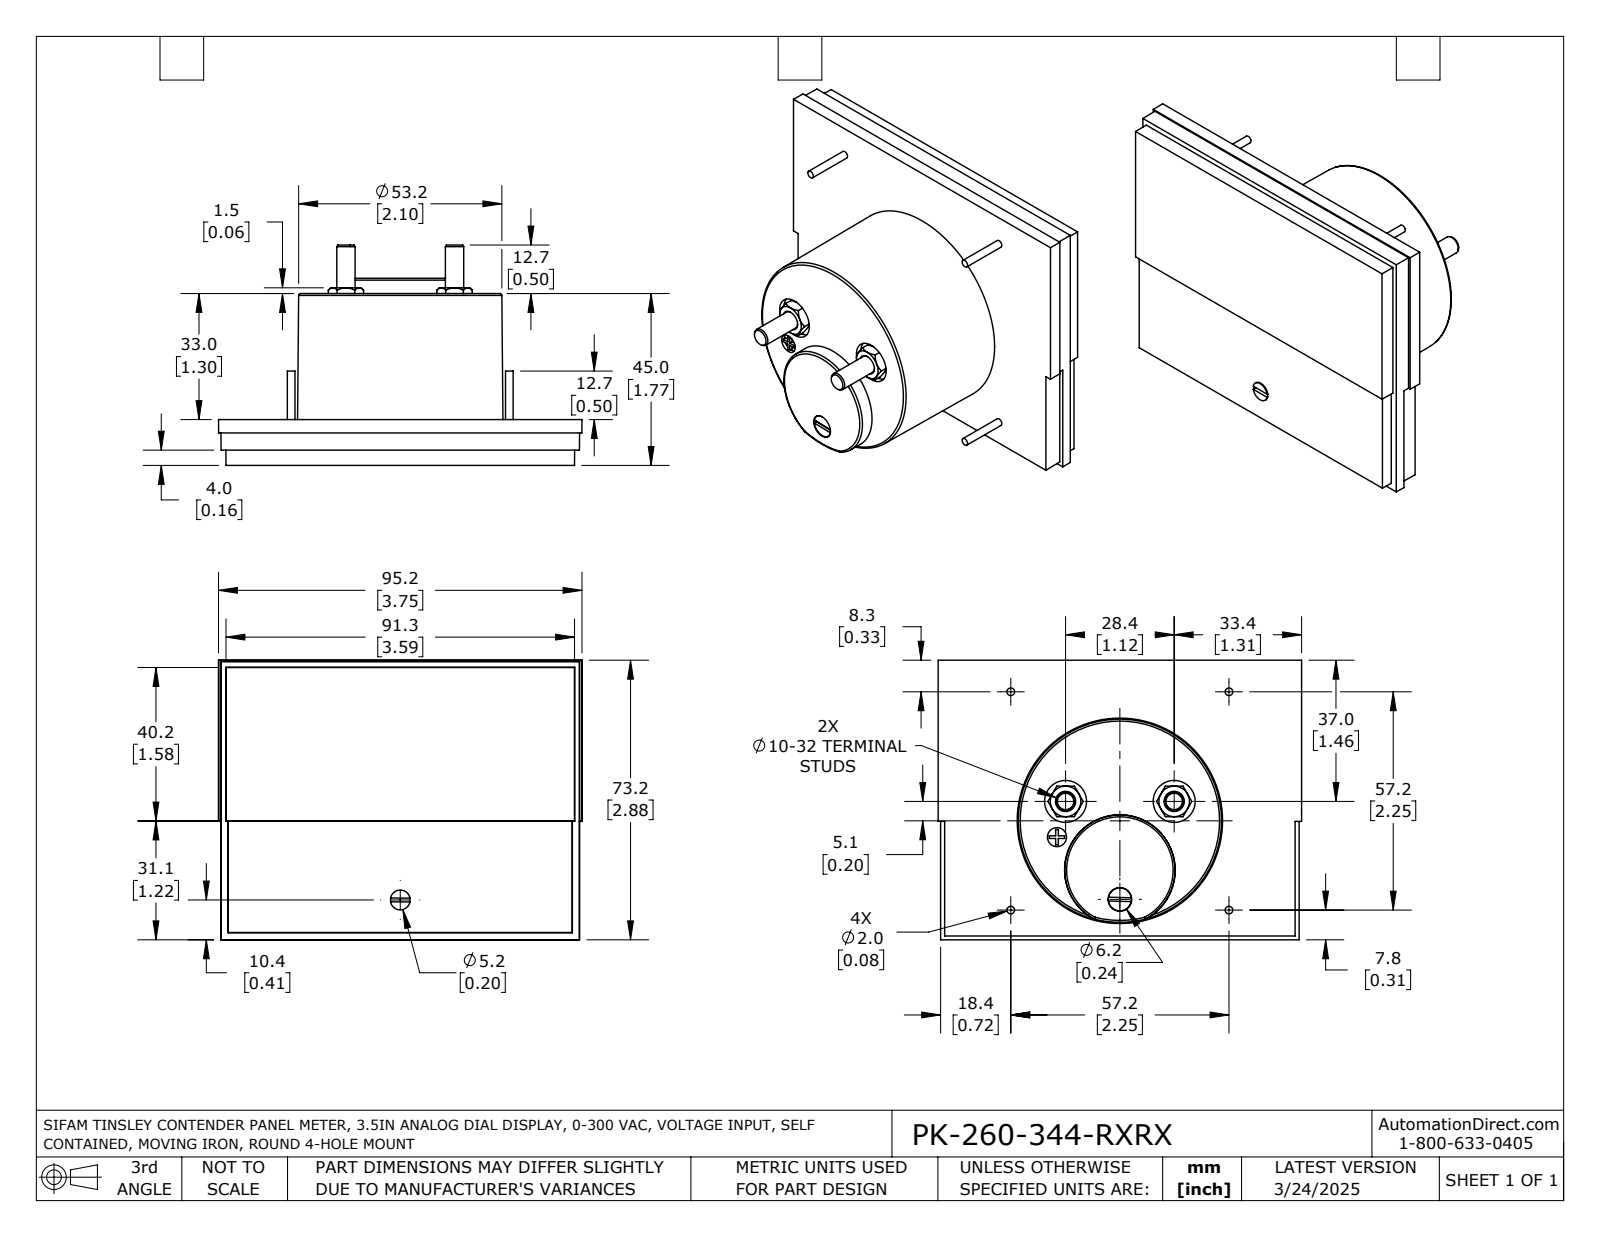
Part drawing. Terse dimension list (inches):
name: PK-260-344-RXRX
written by: SolidWorks 2021 (AUTOMOTIVE_DESIGN)
unit: in
bodies: 1 solid, 163 faces (76 planar, 31 cylindrical, 56 other)
size: 3.748 × 2.882 × 2.272
volume: 9.446 in³; area: 38.39 in²
holes: 2× ⌀0.433, 1× ⌀0.197, 1× ⌀0.244
bosses: 4× ⌀0.079, 2× ⌀0.189, 1× ⌀0.236, 1× ⌀0.205
rounds: 1× R0.1
face distances: 0.472, 0.03, 0.443, 1.772, 1.299, 1.742, 0.157, 0.073, 0.315, 1.457
hole spacings: 1.155, 0.379, 0.912, 1.12, 1.263
